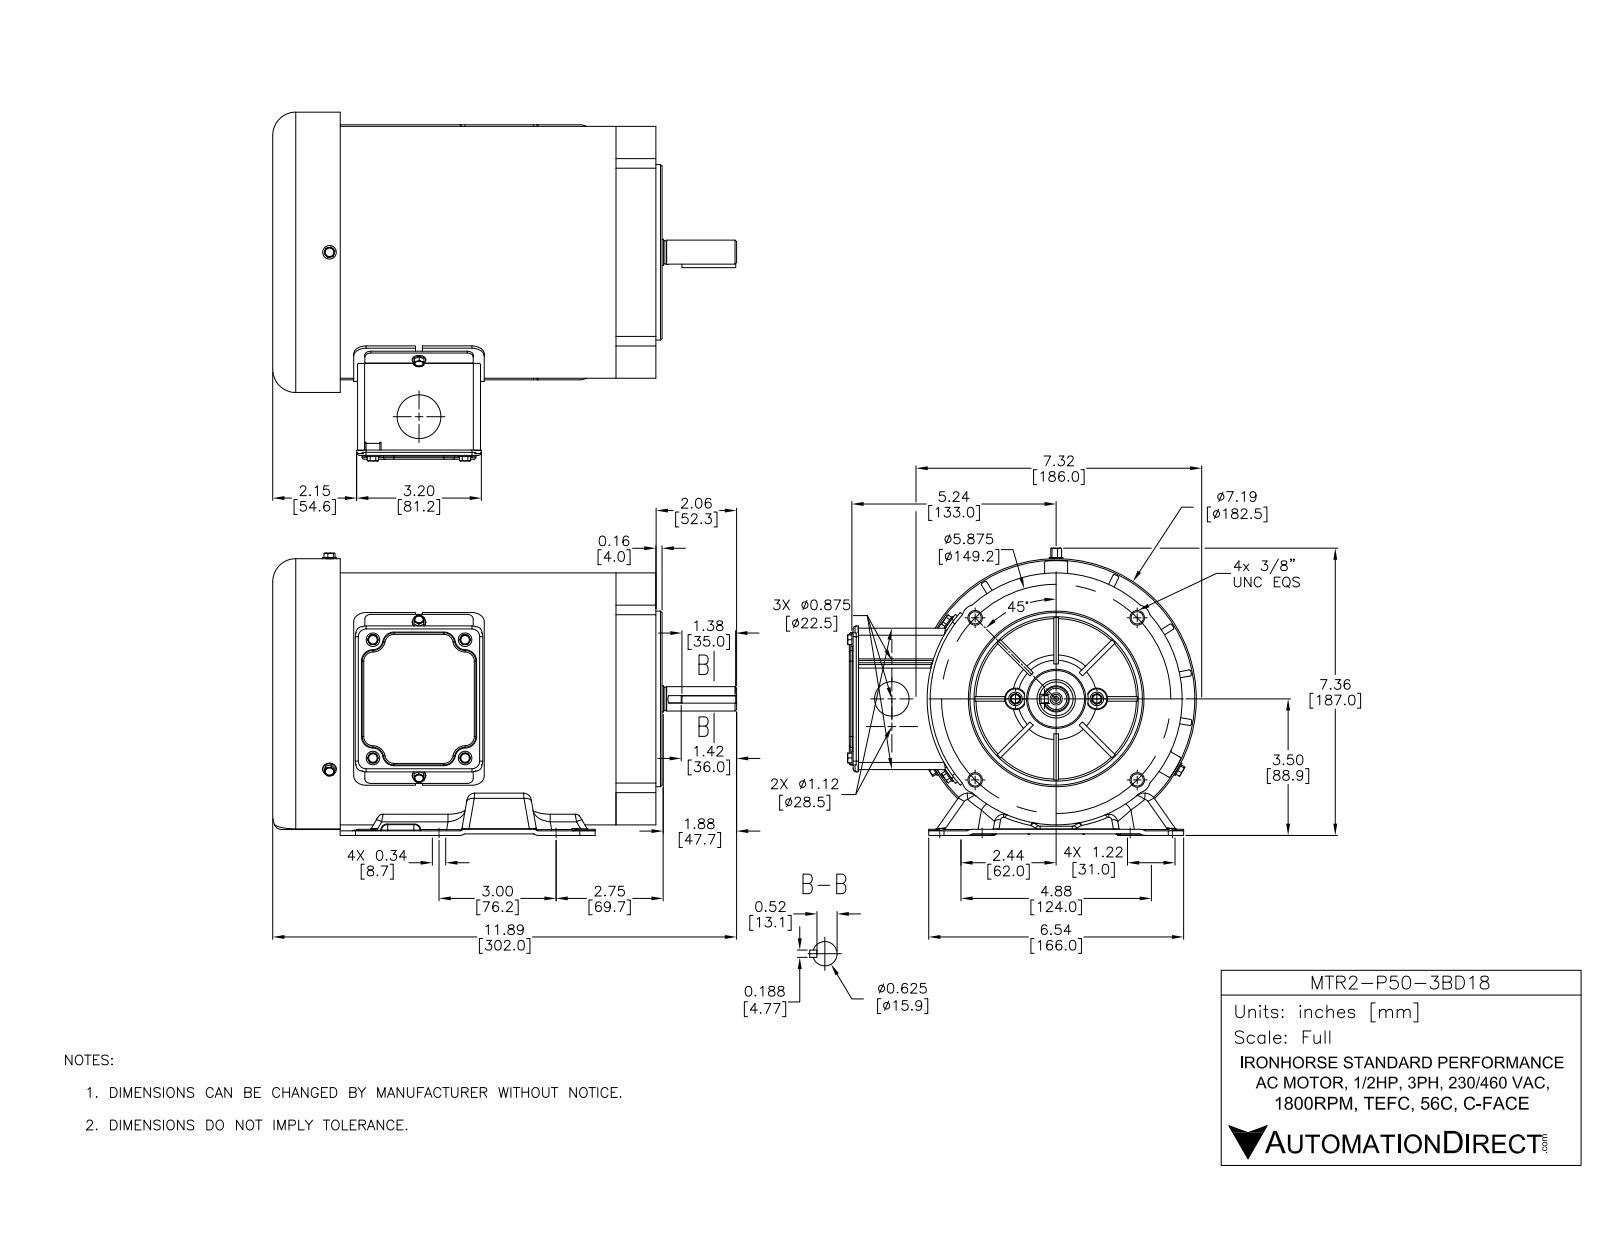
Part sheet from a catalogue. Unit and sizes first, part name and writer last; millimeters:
Units: millimetres
Overall size (bounding box): 295.5 × 227 × 183.7
Round holes (diameter × count): ⌀5 ×12, ⌀5.6 ×11, ⌀7 ×8, ⌀5.5 ×6, ⌀8.7 ×6, ⌀3.5 ×5, ⌀3.8 ×4, ⌀4.5 ×4, ⌀8 ×4, ⌀1.7 ×2, ⌀3.4 ×2, ⌀13 ×2
Round bosses / shafts (diameter × count): ⌀4.2 ×11, ⌀8.8 ×7, ⌀6.4 ×6, ⌀8.8 ×4, ⌀182.5 ×1, ⌀164 ×1, ⌀114.3 ×1, ⌀24 ×1
Partial cylindrical surfaces — rounded edges, fillets, slot ends (radius × count): R3 ×121, R1 ×38, R0.5 ×32, R4 ×32, R3.5 ×26, R7 ×19, R4.4 ×12, R5 ×12
Main face-to-face distances: 3, 1, 1.6, 213, 26, 29, 242, 243, 90.4, 2
Hole centre spacings: 107.2, 77, 2.4, 58.9, 61.2, 74.6, 75.7, 95.2
Volume: 795 600 mm³ · Surface area: 629 900 mm²
Bodies: 37 solids, 2761 faces (763 planar, 888 cylindrical, 1110 other)
Part name (STEP PRODUCT): MTR2-P50-3BD18
STEP written by: SolidWorks 2016 (AUTOMOTIVE_DESIGN)
